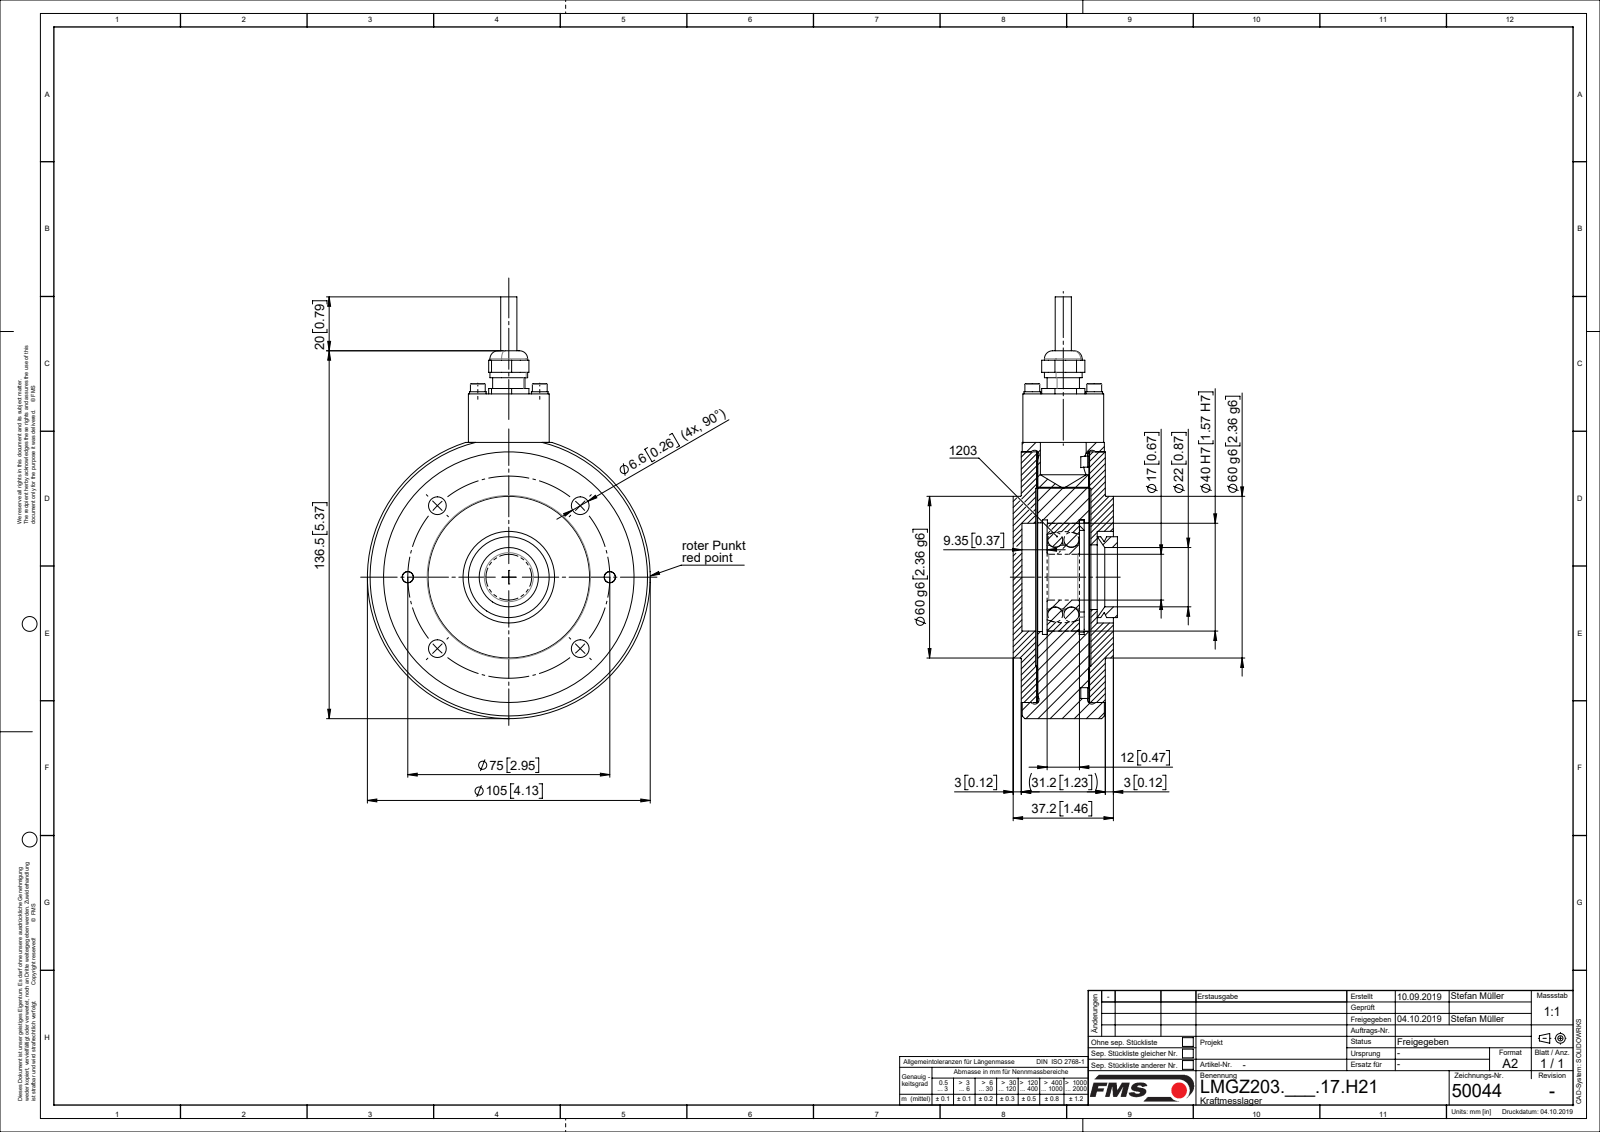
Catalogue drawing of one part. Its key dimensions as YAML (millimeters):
part_name: "ZEICHNUNG6; L50044; L4795904; L47958(1) (+8 more)"
step_written_by: "Mechanical Desktop 2007 (CONFIG_CONTROL_DESIGN)"
units: millimeters
bodies: {solids: 20, faces: 352, planar: 115, cylindrical: 193, other: 44}
overall_size: [136.5, 105, 37.2]
volume: 265121
surface_area: 97422
round_holes:
  - {diameter: 2.6, count: 4}
  - {diameter: 3.2, count: 4}
  - {diameter: 3.4, count: 4}
  - {diameter: 6.6, count: 4}
  - {diameter: 5.5, count: 3}
  - {diameter: 4, count: 2}
  - {diameter: 5.3, count: 2}
  - {diameter: 10, count: 2}
  - {diameter: 6, count: 1}
  - {diameter: 11.28, count: 1}
  - {diameter: 17, count: 1}
  - {diameter: 22, count: 1}
round_bosses_or_shafts:
  - {diameter: 6.2, count: 4}
  - {diameter: 5.5, count: 4}
  - {diameter: 3, count: 4}
  - {diameter: 8, count: 2}
  - {diameter: 5, count: 2}
  - {diameter: 105, count: 1}
  - {diameter: 93, count: 1}
  - {diameter: 60, count: 1}
partial_cylinders:
  - {radius: 2, count: 1}
face_to_face_distances: [19.25, 5.85, 25.1, 19, 6.1, 25.35, 19.5, 3, 19.75, 20]
hole_center_spacings: [37.5, 16.26, 23, 75, 28.69, 28.7, 69.29, 69.3]
